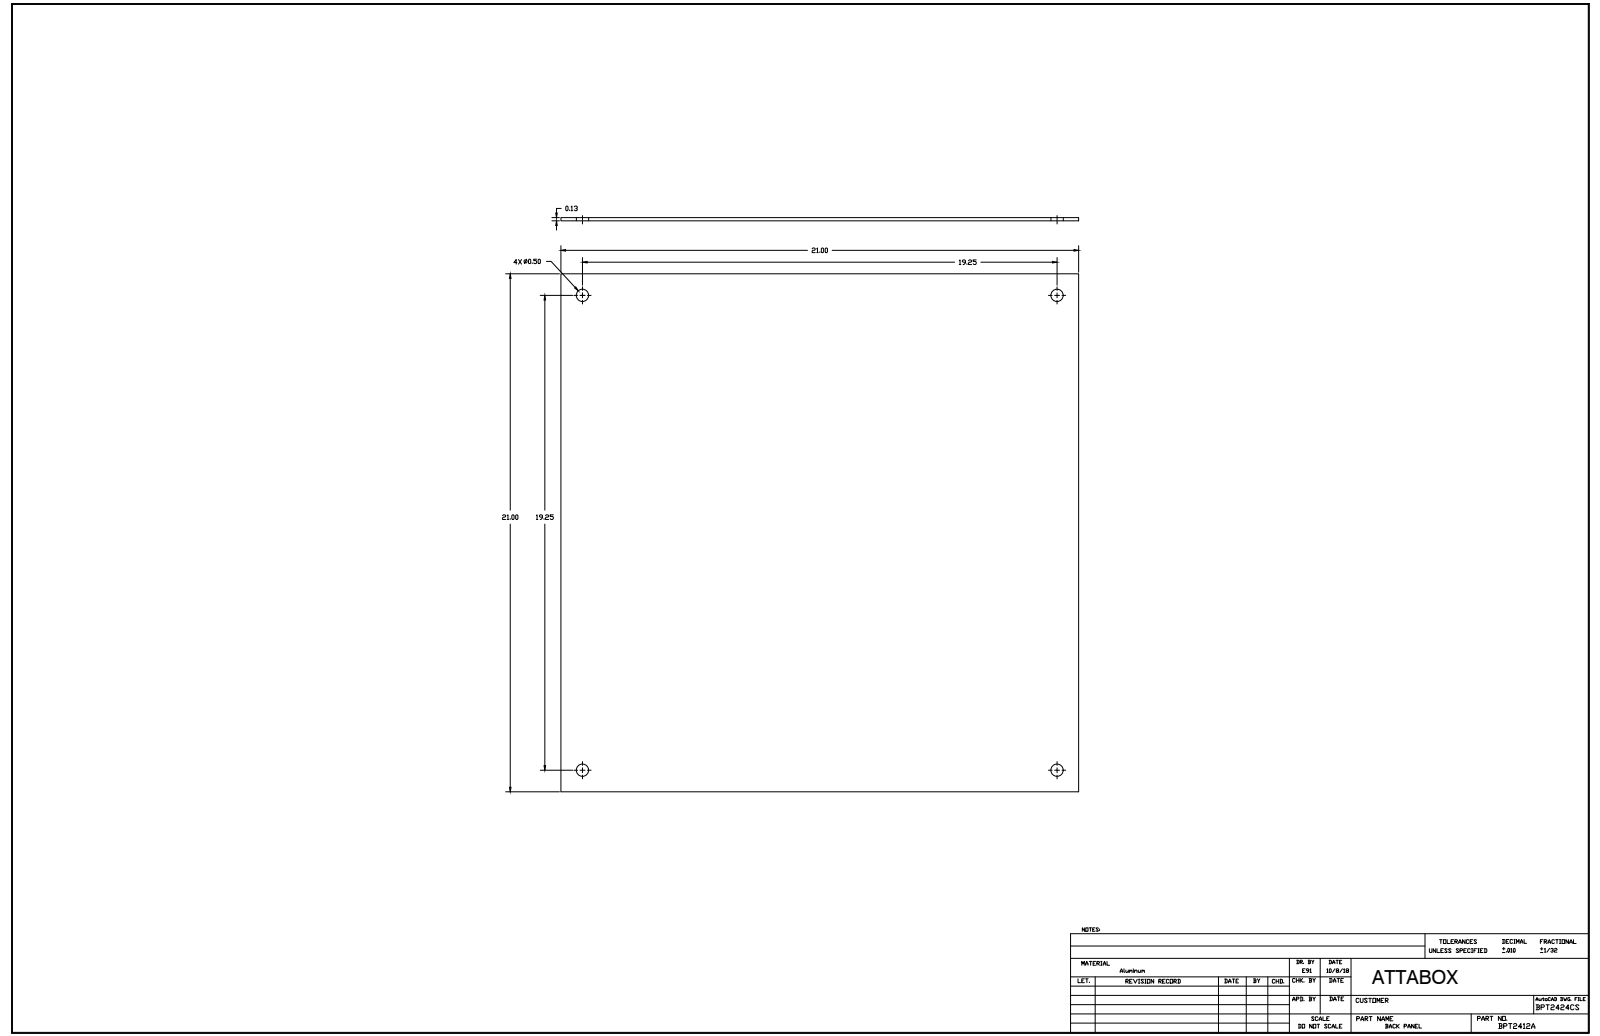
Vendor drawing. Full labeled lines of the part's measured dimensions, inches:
Part name (STEP PRODUCT): HW-WM2424A
STEP written by: SolidWorks 2014 (AUTOMOTIVE_DESIGN)
Units: inches
Bodies: 1 solid, 14 faces (6 planar, 8 cylindrical, 0 other)
Overall size (bounding box): 21 × 21 × 0.13
Volume: 57.23 in³ · Surface area: 892.2 in²
Round holes (diameter × count): ⌀0.5 ×4
Main face-to-face distances: 0.13, 21
Hole centre spacings: 19.25, 19.25, 27.223
